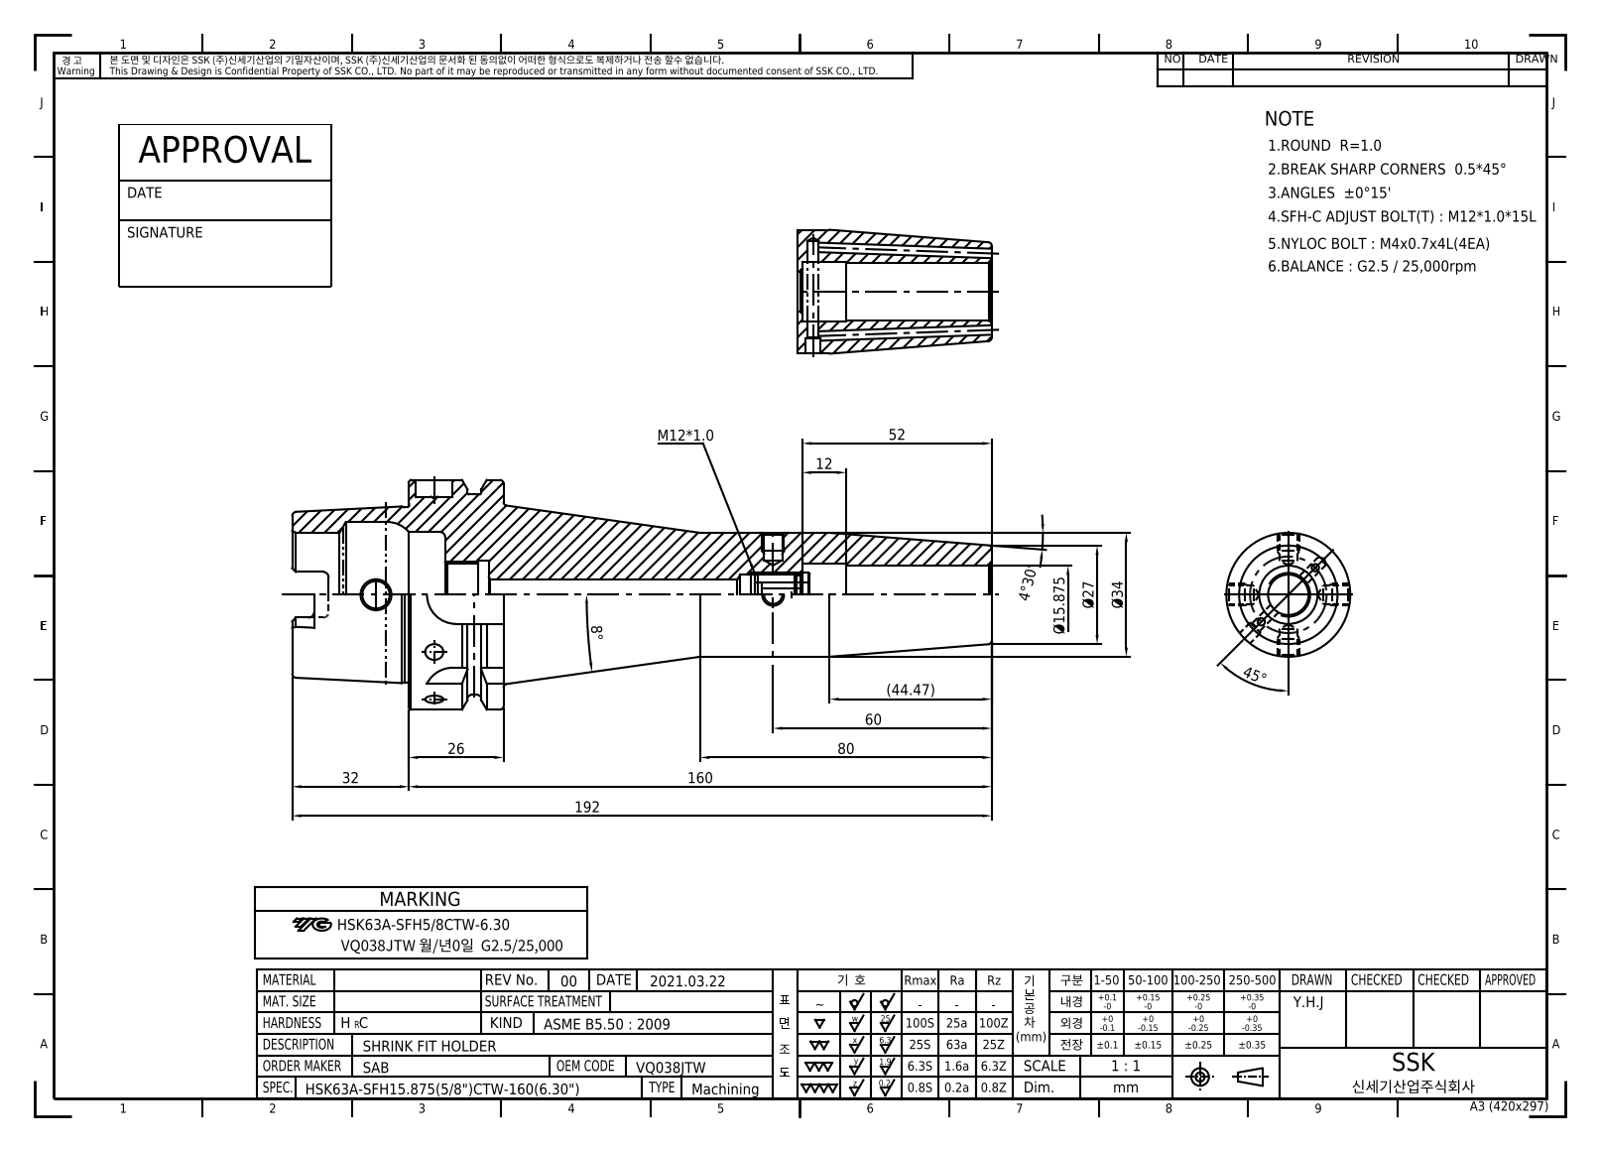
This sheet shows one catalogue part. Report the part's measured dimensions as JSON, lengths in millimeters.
{"part_name": "HSK63A_BALANCE_20200217", "step_written_by": "CREO PARAMETRIC BY PTC INC, 2018500 (CONFIG_CONTROL_DESIGN)", "units": "millimeters", "bodies": {"solids": 1, "faces": 186, "planar": 57, "cylindrical": 57, "other": 72}, "overall_size": [192, 63, 63], "volume_mm3": 204039, "surface_area_mm2": 42499, "round_holes": [[5, 2], [7.5, 1], [8.4, 1], [10, 1], [11, 1], [12, 1], [15.88, 1], [17, 1], [17.07, 1], [18, 1], [19, 1], [34, 1]], "round_bosses_or_shafts": [[63, 1], [55, 1], [48.04, 1]], "partial_cylinders_radius": [[1.5, 6], [2.88, 4], [8, 4]], "face_to_face_distances": [26, 10, 16, 32, 6.12, 9.88, 42, 58, 4, 134]}
